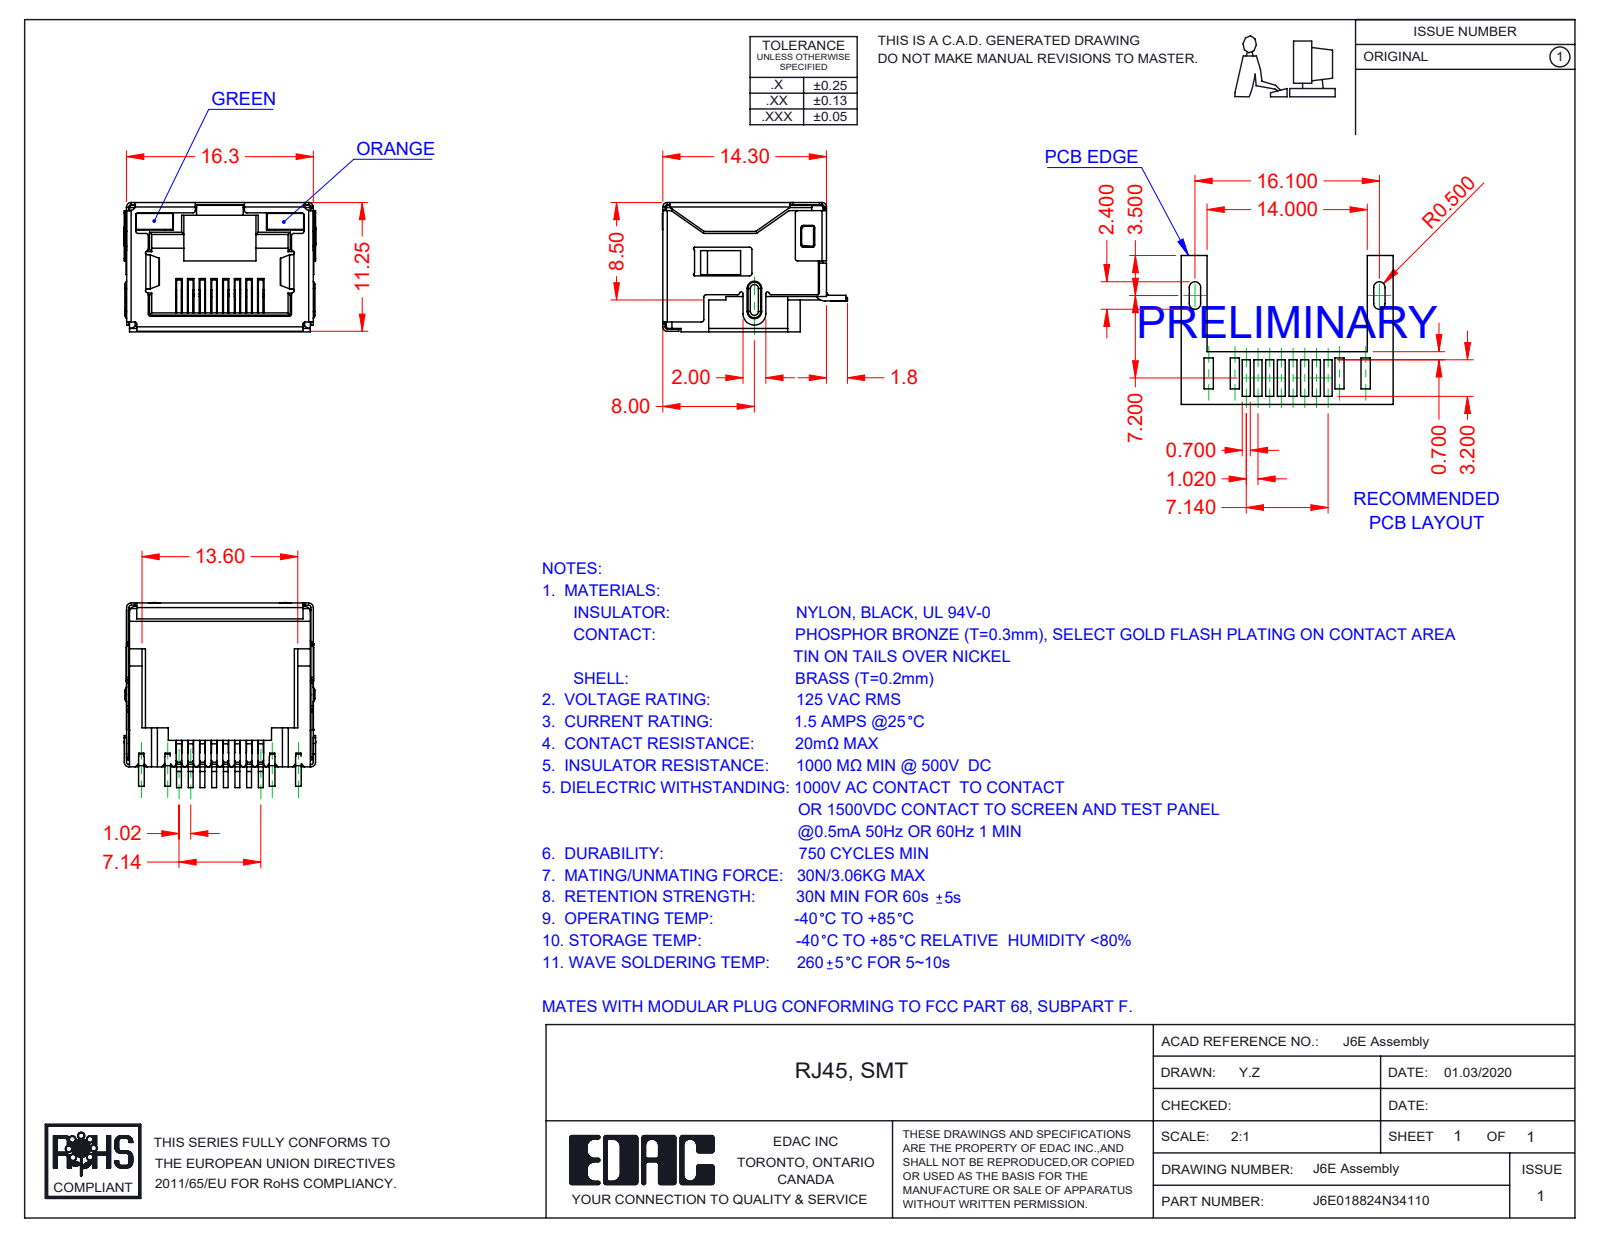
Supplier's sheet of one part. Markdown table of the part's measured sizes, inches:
| quantity | value |
| --- | --- |
| part name | 6E Insulator_LED; 6E LED RH_4-Orange; 6E LED LH_3-Green; 6E Shield_LED (+2 more) |
| STEP written by | SolidWorks 2016 (CONFIG_CONTROL_DESIGN) |
| units | inches |
| bodies | 12 solids, 1496 faces (1099 planar, 347 cylindrical, 50 other) |
| overall size | 0.659 × 0.636 × 0.445 |
| volume | 0.068 in³ |
| surface area | 6.27 in² |
| partial cylindrical surfaces (radius × count) | 0.008 × 82, 0.01 × 17, 0.016 × 13, 0.02 × 13, 0.004 × 10, 0.006 × 7, 0.012 × 4, 0.039 × 3 |
| main face-to-face distances | 0.435, 0.632, 0.634, 0.624, 0.437, 0.445, 0.094, 0.028, 0.388, 0.019 |
